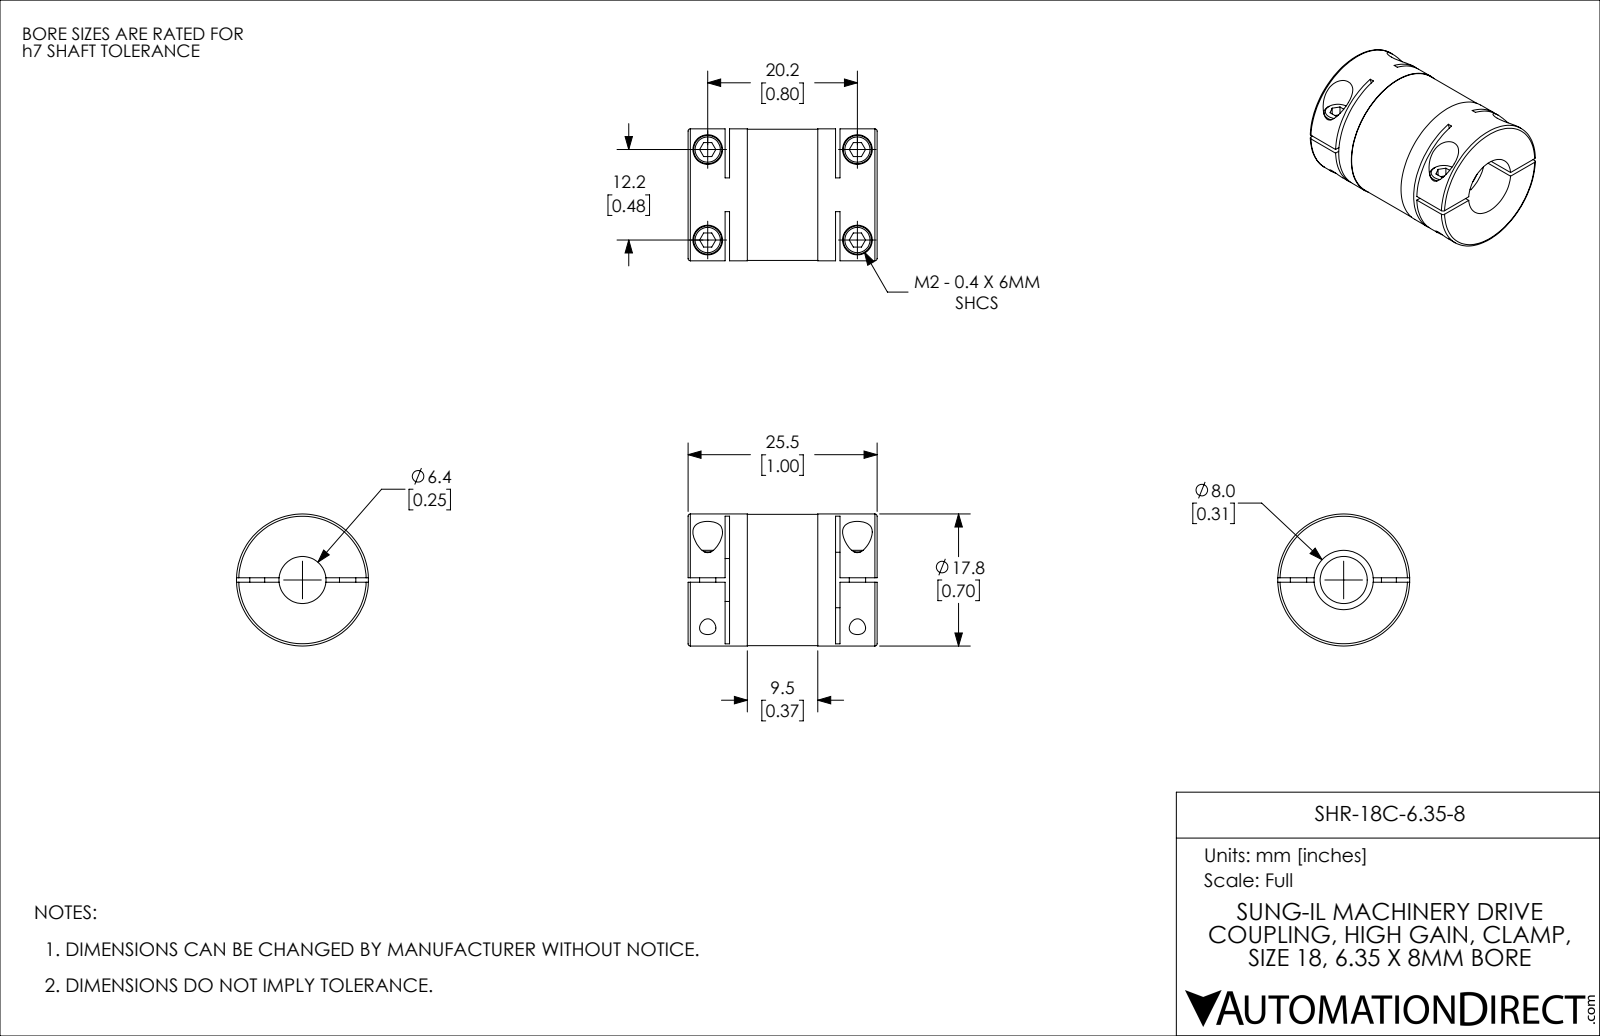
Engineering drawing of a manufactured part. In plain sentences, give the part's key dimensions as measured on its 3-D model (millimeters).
The part is named "SHR-18C-6.35-8". Its 3-D file was written by "SolidWorks 2021 (CONFIG_CONTROL_DESIGN)". It is 1 solid with 146 faces: 70 planar, 56 cylindrical and 20 other. Overall it measures 25.5 by 17.8 by 17.8 millimeters. Its volume is 4 484 cubic millimeters and its surface area 3 858 square millimeters. Round holes: 4 of diameter 2.2, 4 of diameter 4, 1 of diameter 6.35, 1 of diameter 8, 1 of diameter 10. Round bosses or shafts: 4 of diameter 3.8, 2 of diameter 2, 1 of diameter 17.8, 1 of diameter 17.7. Partial cylindrical surfaces (rounded edges, fillets, slot ends): 2 of radius 35. The main face-to-face distances are 0.6, 5.6, 19.9, 5, 20.5, 14.9, 25.5, 14.3, 15.5, 17.5. The hole center spacings are 12.2, 20.2, 23.6.
